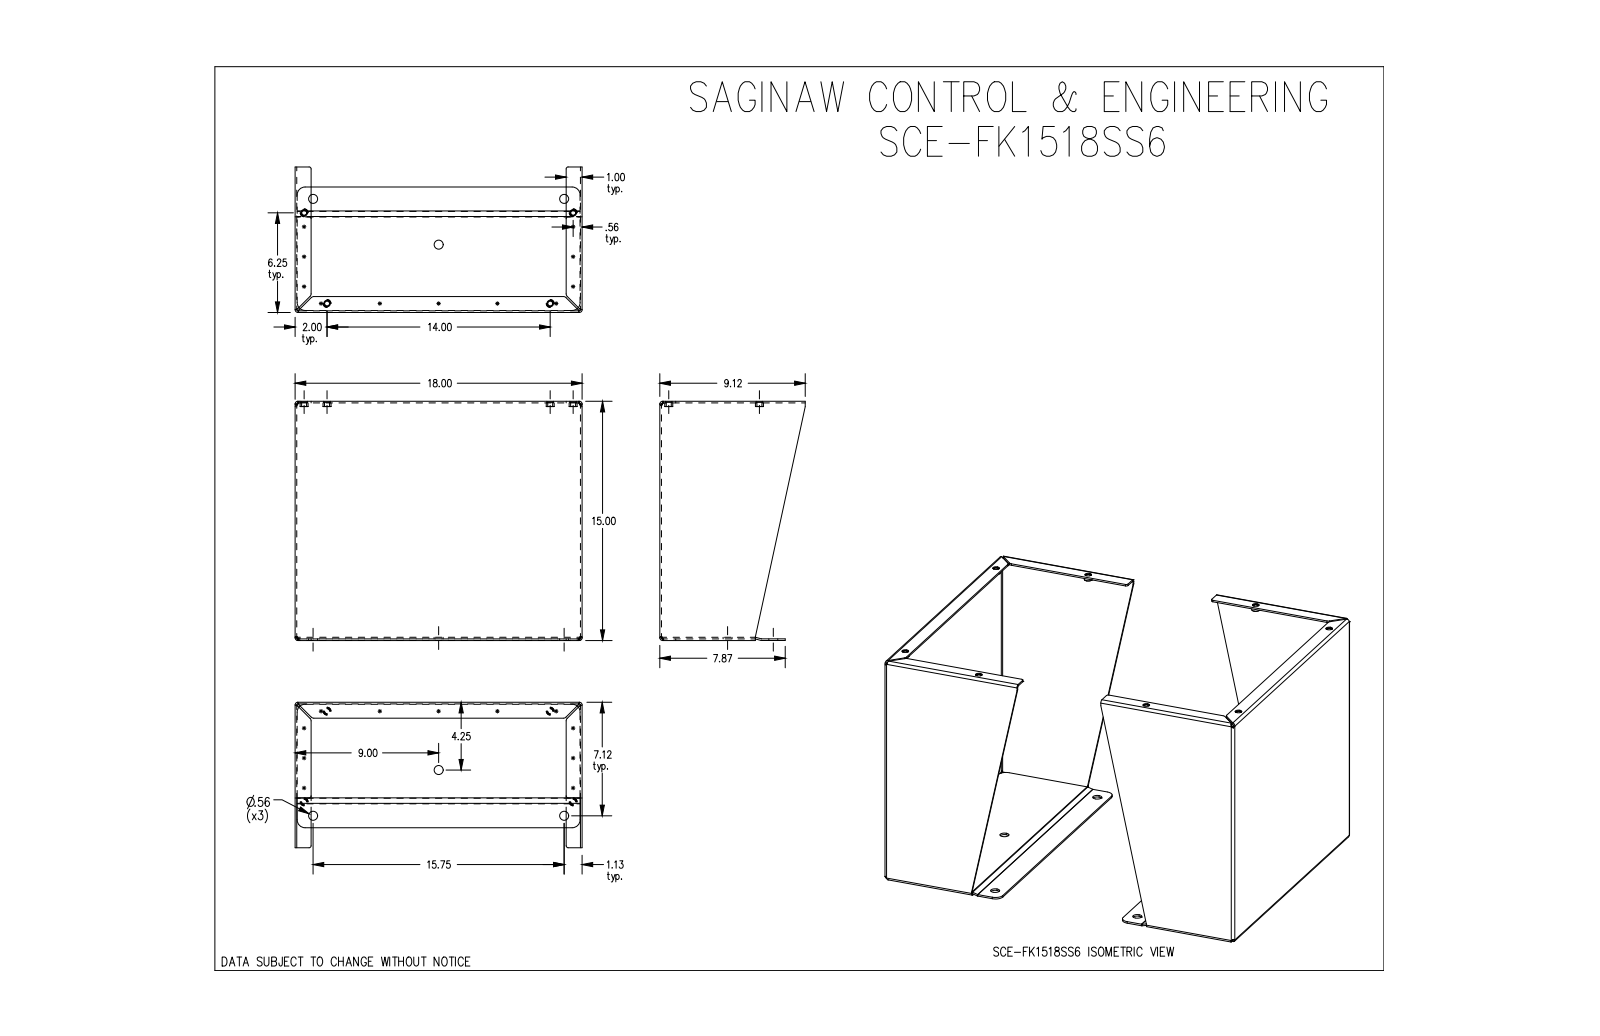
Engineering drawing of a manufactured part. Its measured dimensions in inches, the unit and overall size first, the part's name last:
Units: inches
Overall size (bounding box): 24 × 18 × 15
Round holes (diameter × count): ⌀0.312 ×8, ⌀0.413 ×8, ⌀0.563 ×6
Round bosses / shafts (diameter × count): ⌀0.5 ×8, ⌀0.412 ×8
Partial cylindrical surfaces — rounded edges, fillets, slot ends (radius × count): R0.166 ×16, R0.062 ×12, R0.125 ×8, R0.22 ×8, R0.5 ×8, R0.063 ×6
Main face-to-face distances: 0.104, 23.896, 17.896, 24, 23.792, 18, 17.792, 14.792, 0.101, 14.893
Hole centre spacings: 1.035, 5.866, 6.614, 7.913, 8.671, 10.646, 14.884, 15.919
Volume: 141.7 in³ · Surface area: 2 762 in²
Bodies: 12 solids, 286 faces (120 planar, 110 cylindrical, 56 other)
Part name (STEP PRODUCT): SCE-FK1518SS6
STEP written by: SolidWorks 2019 (CONFIG_CONTROL_DESIGN)
